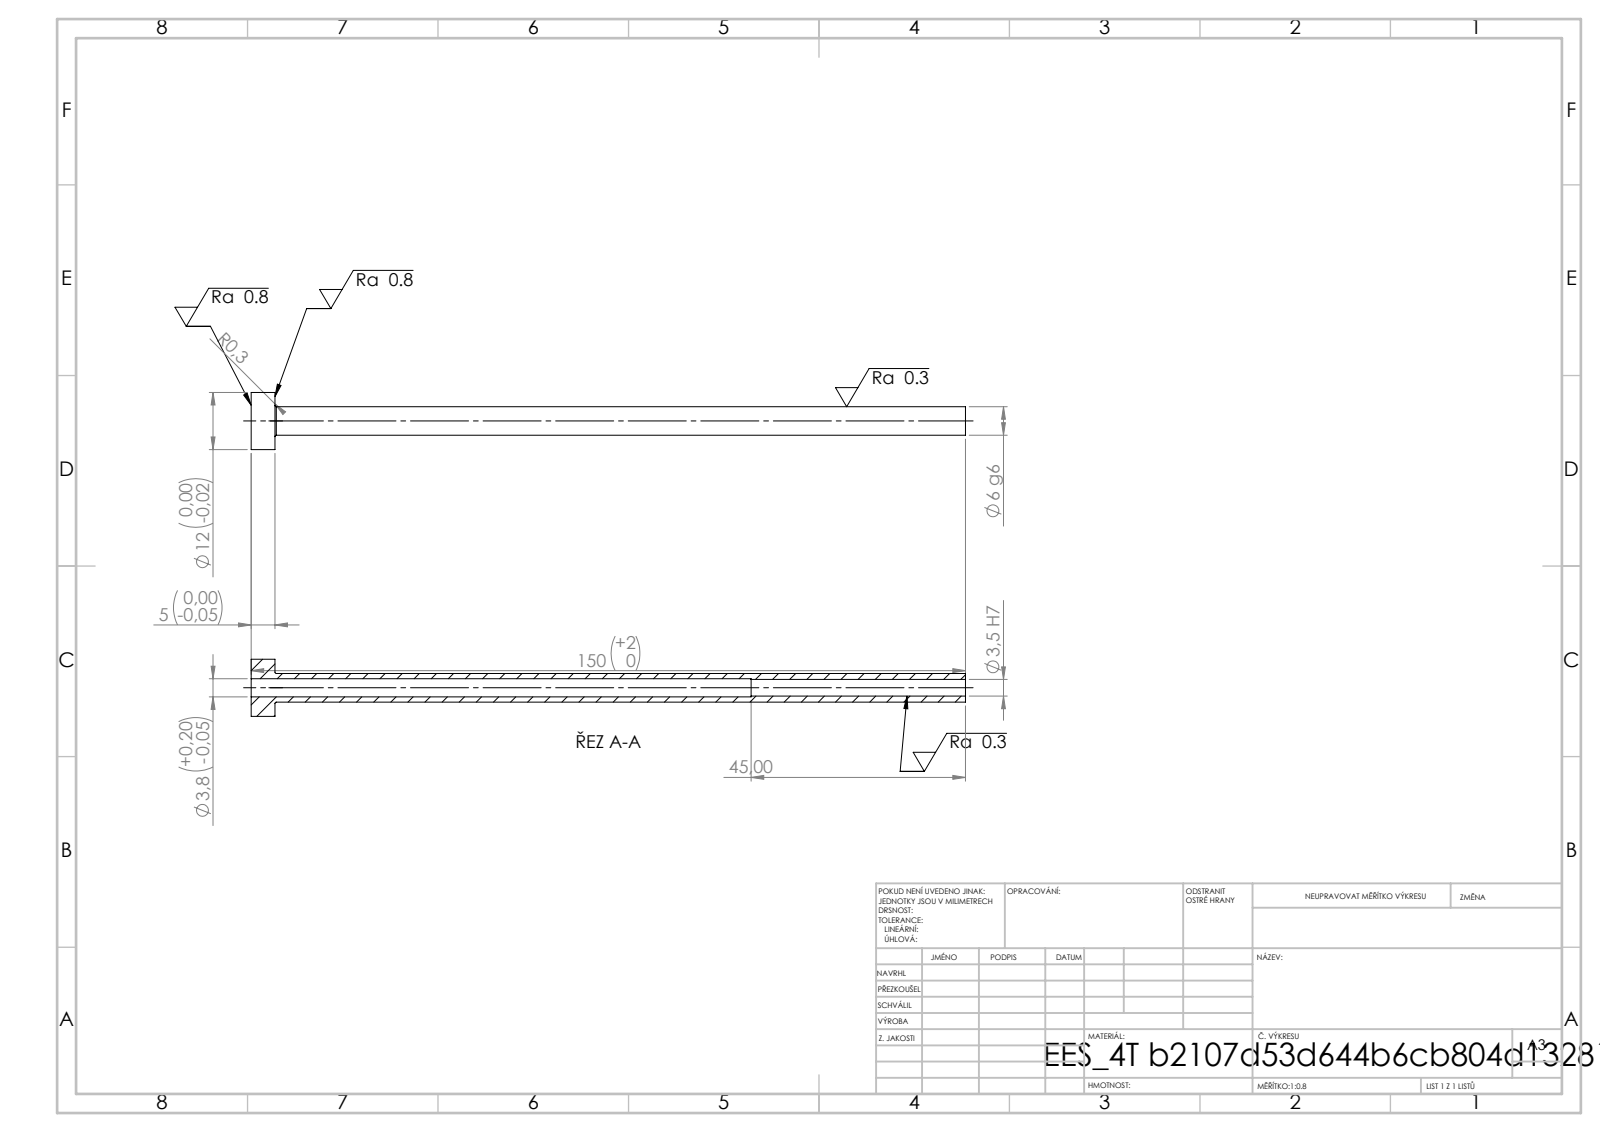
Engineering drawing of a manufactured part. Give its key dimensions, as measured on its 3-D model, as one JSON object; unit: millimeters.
{"step_written_by": "SolidWorks 2019 (CONFIG_CONTROL_DESIGN)", "units": "millimeters", "bodies": {"solids": 1, "faces": 14, "planar": 4, "cylindrical": 8, "other": 2}, "overall_size": [150, 12, 12], "volume_mm3": 3042, "surface_area_mm2": 4875, "round_holes": [[3.5, 1], [3.8, 1]], "round_bosses_or_shafts": [[12, 1], [6, 1]], "face_to_face_distances": [5, 150, 145, 105, 100, 45]}
